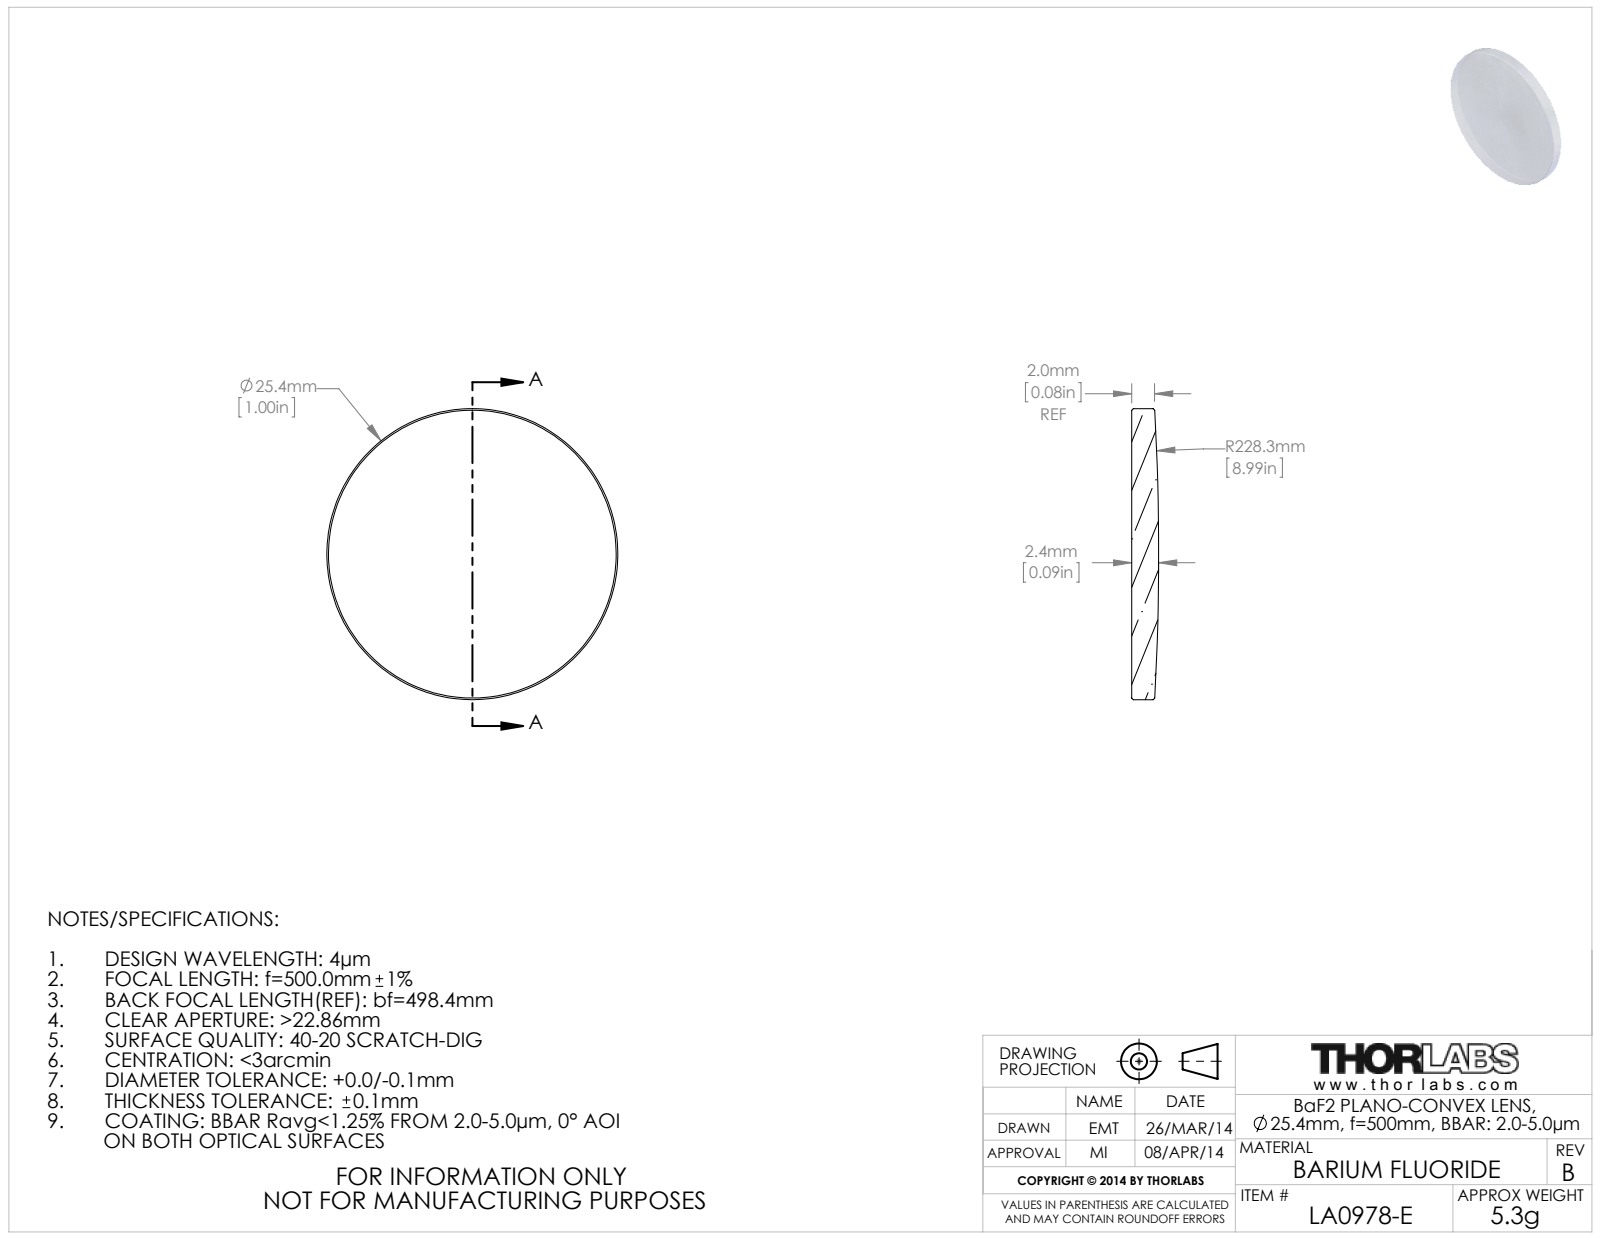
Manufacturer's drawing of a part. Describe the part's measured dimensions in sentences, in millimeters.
The part is named "20098-E0W". Its 3-D file was written by "SolidWorks 2014 (CONFIG_CONTROL_DESIGN)". It is 1 solid with 9 faces: 1 planar, 2 cylindrical and 6 other. Overall it measures 25.4 by 25.4 by 2.35 millimeters. Its volume is 1 100 cubic millimeters and its surface area 1 160 square millimeters. Round bosses or shafts: 1 of diameter 25.4.
